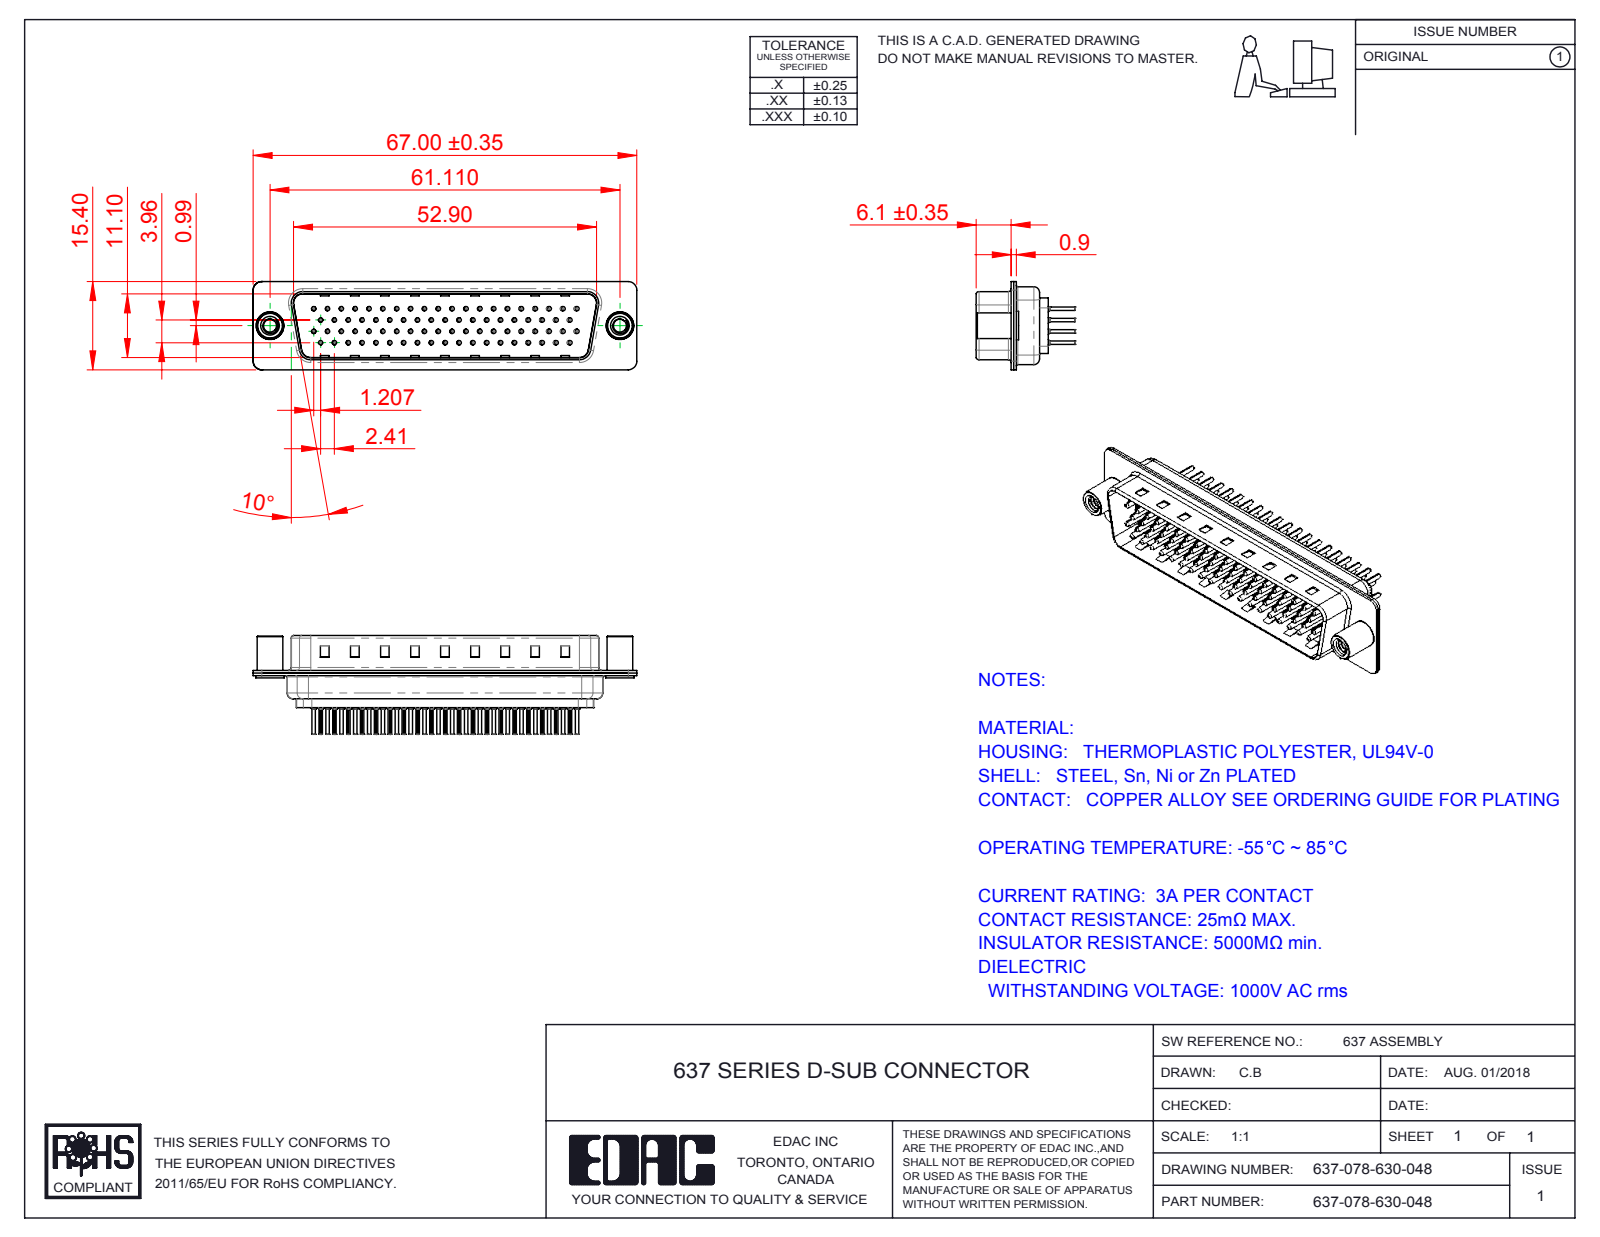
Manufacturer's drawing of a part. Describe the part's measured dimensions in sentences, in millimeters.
The part is named "637 Contact Row 3_30; 637 Contact Row 78_30; 637 Shell Rear_78 Contacts; 637-078-630-048 (+5 more)". Its 3-D file was written by "SolidWorks 2016 (CONFIG_CONTROL_DESIGN)". It is 83 solids with 8246 faces: 2077 planar, 3055 cylindrical and 3114 other. Overall it measures 67 by 17.25 by 15.4 millimeters. Its volume is 4 398 cubic millimeters and its surface area 16 058 square millimeters. Round holes: 150 of diameter 1.6, 78 of diameter 0.2, 78 of diameter 0.35, 78 of diameter 1.1, 72 of diameter 0.75, 72 of diameter 2, 3 of diameter 4, 2 of diameter 2.26, 2 of diameter 4.8. Round bosses or shafts: 78 of diameter 2, 78 of diameter 1.5, 78 of diameter 0.75, 78 of diameter 0.6, 2 of diameter 5, 2 of diameter 4.9, 2 of diameter 4.5, 1 of diameter 4.8. Partial cylindrical surfaces (rounded edges, fillets, slot ends): 156 of radius 0.1, 16 of radius 1.5, 12 of radius 2, 8 of radius 0.5, 4 of radius 0.25, 4 of radius 0.55, 4 of radius 0.7, 4 of radius 0.95. The main face-to-face distances are 0.45, 0.4, 1.5, 1.95, 11.9, 11.5, 0.7, 11.1, 0.9, 0.8. The hole center spacings are 2.41, 7.24, 6.06, 9.65, 6.96, 8.46, 14.54, 16.89.
